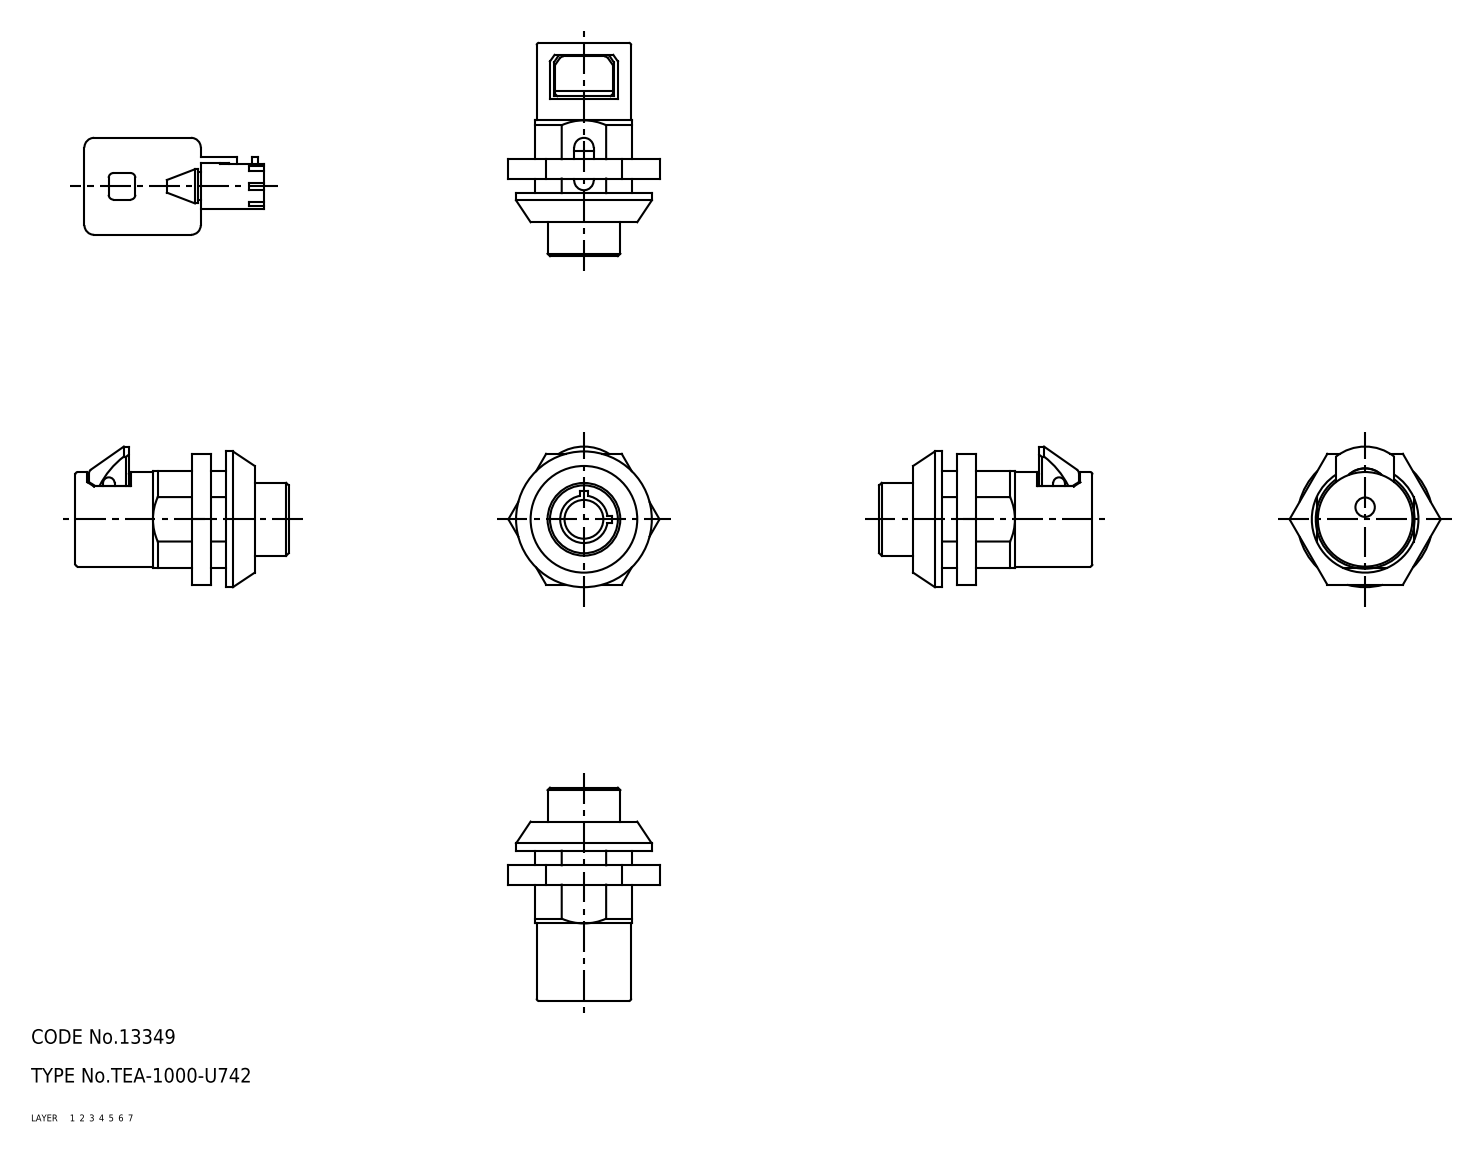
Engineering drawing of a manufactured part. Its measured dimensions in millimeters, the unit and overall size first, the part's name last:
Units: millimetres
Overall size (bounding box): 97 × 31.18 × 29
Volume: 14 378 mm³ · Surface area: 11 377 mm²
Bodies: 4 solids, 178 faces (0 planar, 0 cylindrical, 178 other)
Part name (STEP PRODUCT): key; nut; lock; housing (+1 more)
STEP written by: CADfix (AUTOMOTIVE_DESIGN)
